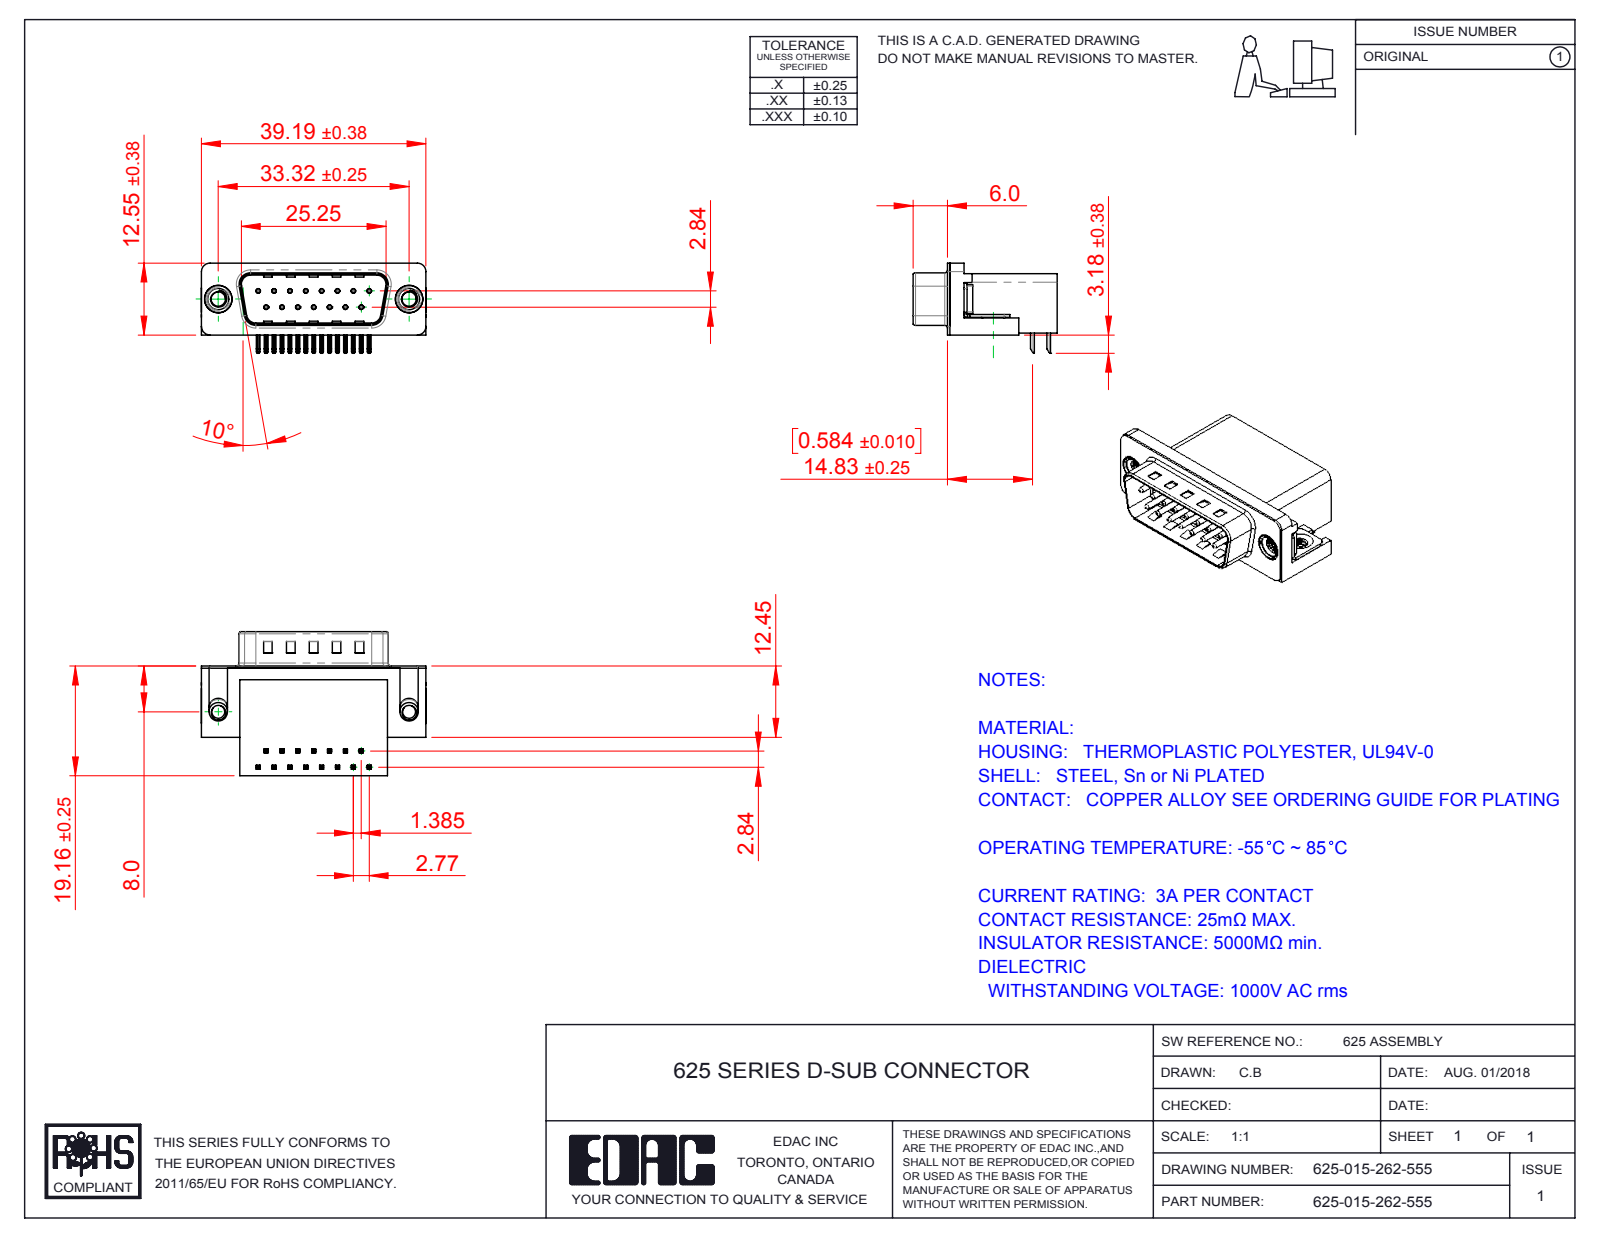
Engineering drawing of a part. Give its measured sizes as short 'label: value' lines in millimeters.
name: 625 M3 Threaded Rivet; 625 4-40 Threaded Board Mount; 625 Housing_15 Socket; 625 Contact Bottom (+3 more)
written by: SolidWorks 2016 (CONFIG_CONTROL_DESIGN)
unit: mm
bodies: 21 solids, 1511 faces (895 planar, 463 cylindrical, 153 other)
size: 39.22 × 25.16 × 15.73
volume: 6 248 mm³; area: 6 507 mm²
holes: 15× ⌀0.35, 15× ⌀0.8, 2× ⌀2.26, 2× ⌀2.5, 2× ⌀4, 2× ⌀4.8, 2× ⌀5
bosses: 15× ⌀0.75, 2× ⌀4.9, 2× ⌀4.75, 2× ⌀3.9, 2× ⌀3.26
rounds: 68× R0.25, 30× R0.12, 16× R1, 9× R0.5, 8× R1.6, 6× R1.5, 4× R0.9, 4× R2
face distances: 0.4, 10.35, 18.76, 2.1, 10.46, 19.16, 1.7, 10.86, 8.76, 16.26
hole spacings: 3.16, 2.77, 5.54, 8.31, 11.08, 5.03, 5.04, 7.48
